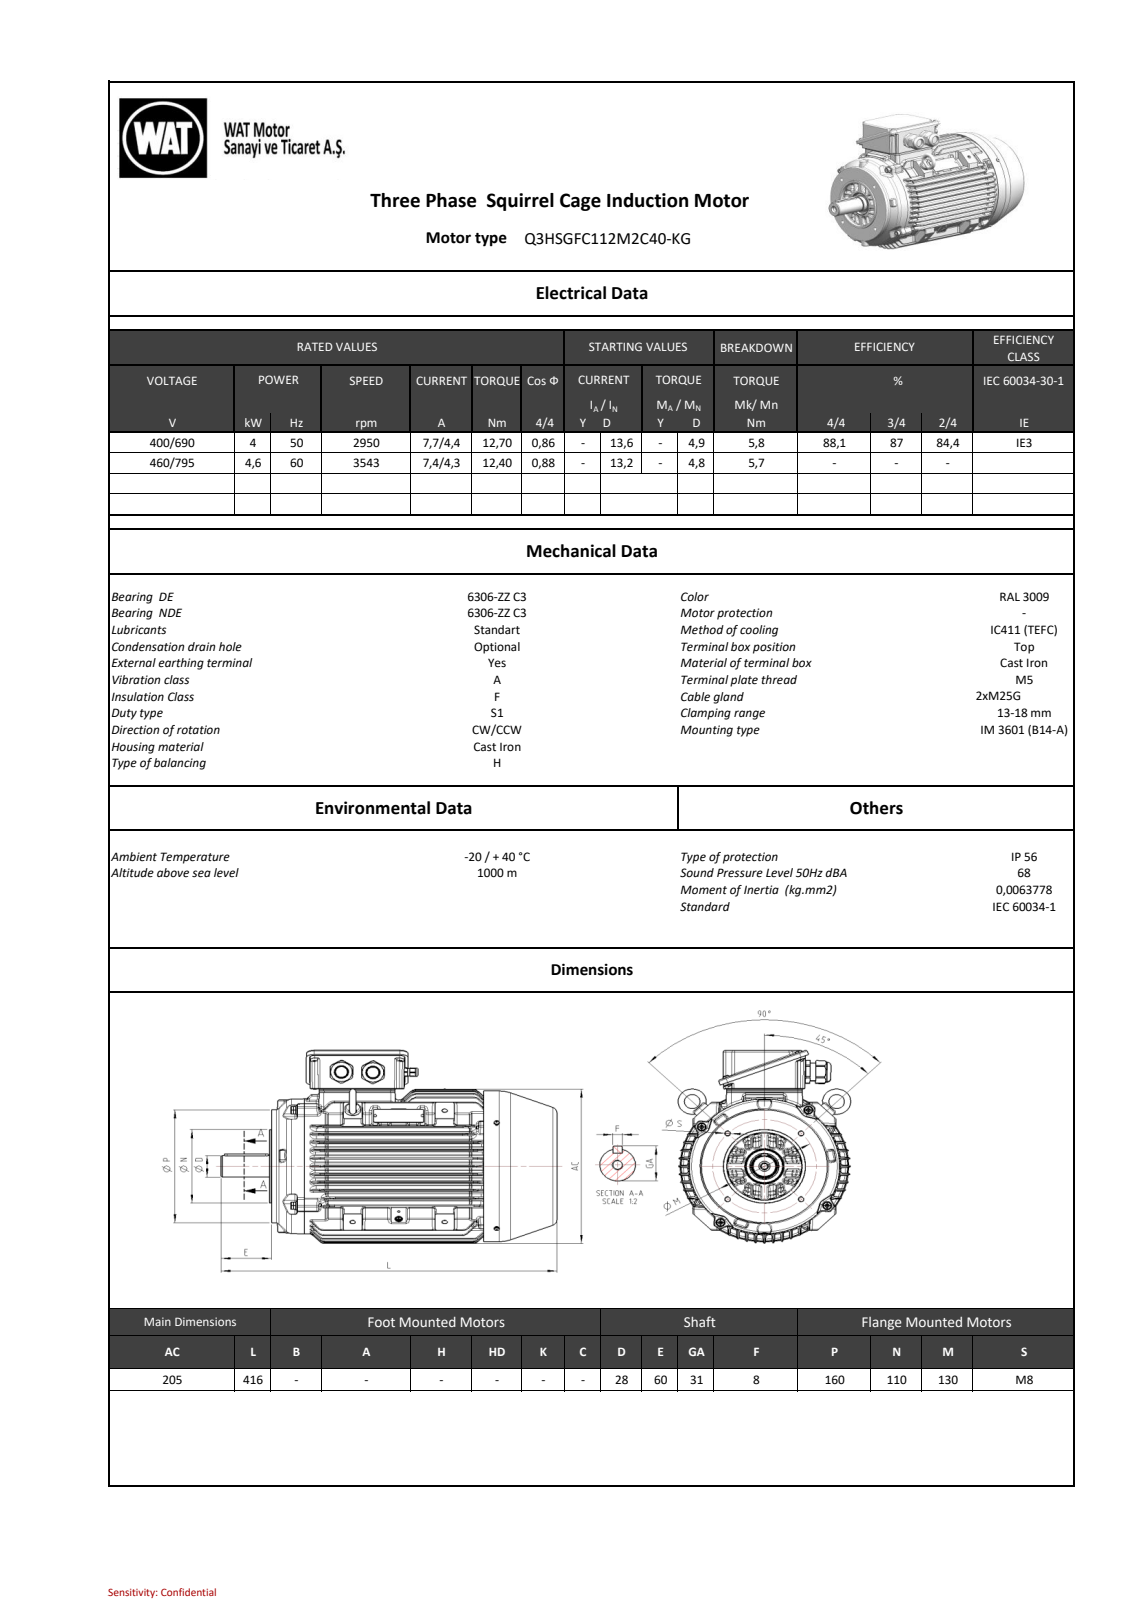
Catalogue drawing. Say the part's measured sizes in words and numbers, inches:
The part is named "260037F440EAovam". Its 3-D file was written by "SIEMENS PLM Software NX 11.0 (AUTOMOTIVE_DESIGN)". It is 0 solids with 4234 faces: 819 planar, 1035 cylindrical and 2380 other. Overall it measures 16.063 by 10.746 by 8.069 inches. Round holes: 10 of diameter 0.268, 8 of diameter 0.197, 3 of diameter 0.394, 2 of diameter 0.098, 2 of diameter 0.165, 1 of diameter 0.157, 1 of diameter 0.256, 1 of diameter 0.335, 1 of diameter 0.413, 1 of diameter 1.709, 1 of diameter 1.717, 1 of diameter 7.756. Round bosses or shafts: 8 of diameter 0.394, 6 of diameter 0.472, 4 of diameter 0.341, 4 of diameter 0.315, 4 of diameter 0.157, 2 of diameter 1.244, 2 of diameter 0.787, 1 of diameter 7.874. Partial cylindrical surfaces (rounded edges, fillets, slot ends): 249 of radius 0.157, 101 of radius 0.059, 77 of radius 0.118, 42 of radius 0.071, 37 of radius 0.039, 34 of radius 0.079, 24 of radius 0.01, 12 of radius 1.043. The main face-to-face distances are 0.533, 1.069, 0.536, 1.608, 1.075, 0.539, 3.104, 2.567, 2.035, 2.15. The hole center spacings are 1.097, 3.524, 3.979, 4.7, 4.983, 6.06, 2.303, 2.815.
